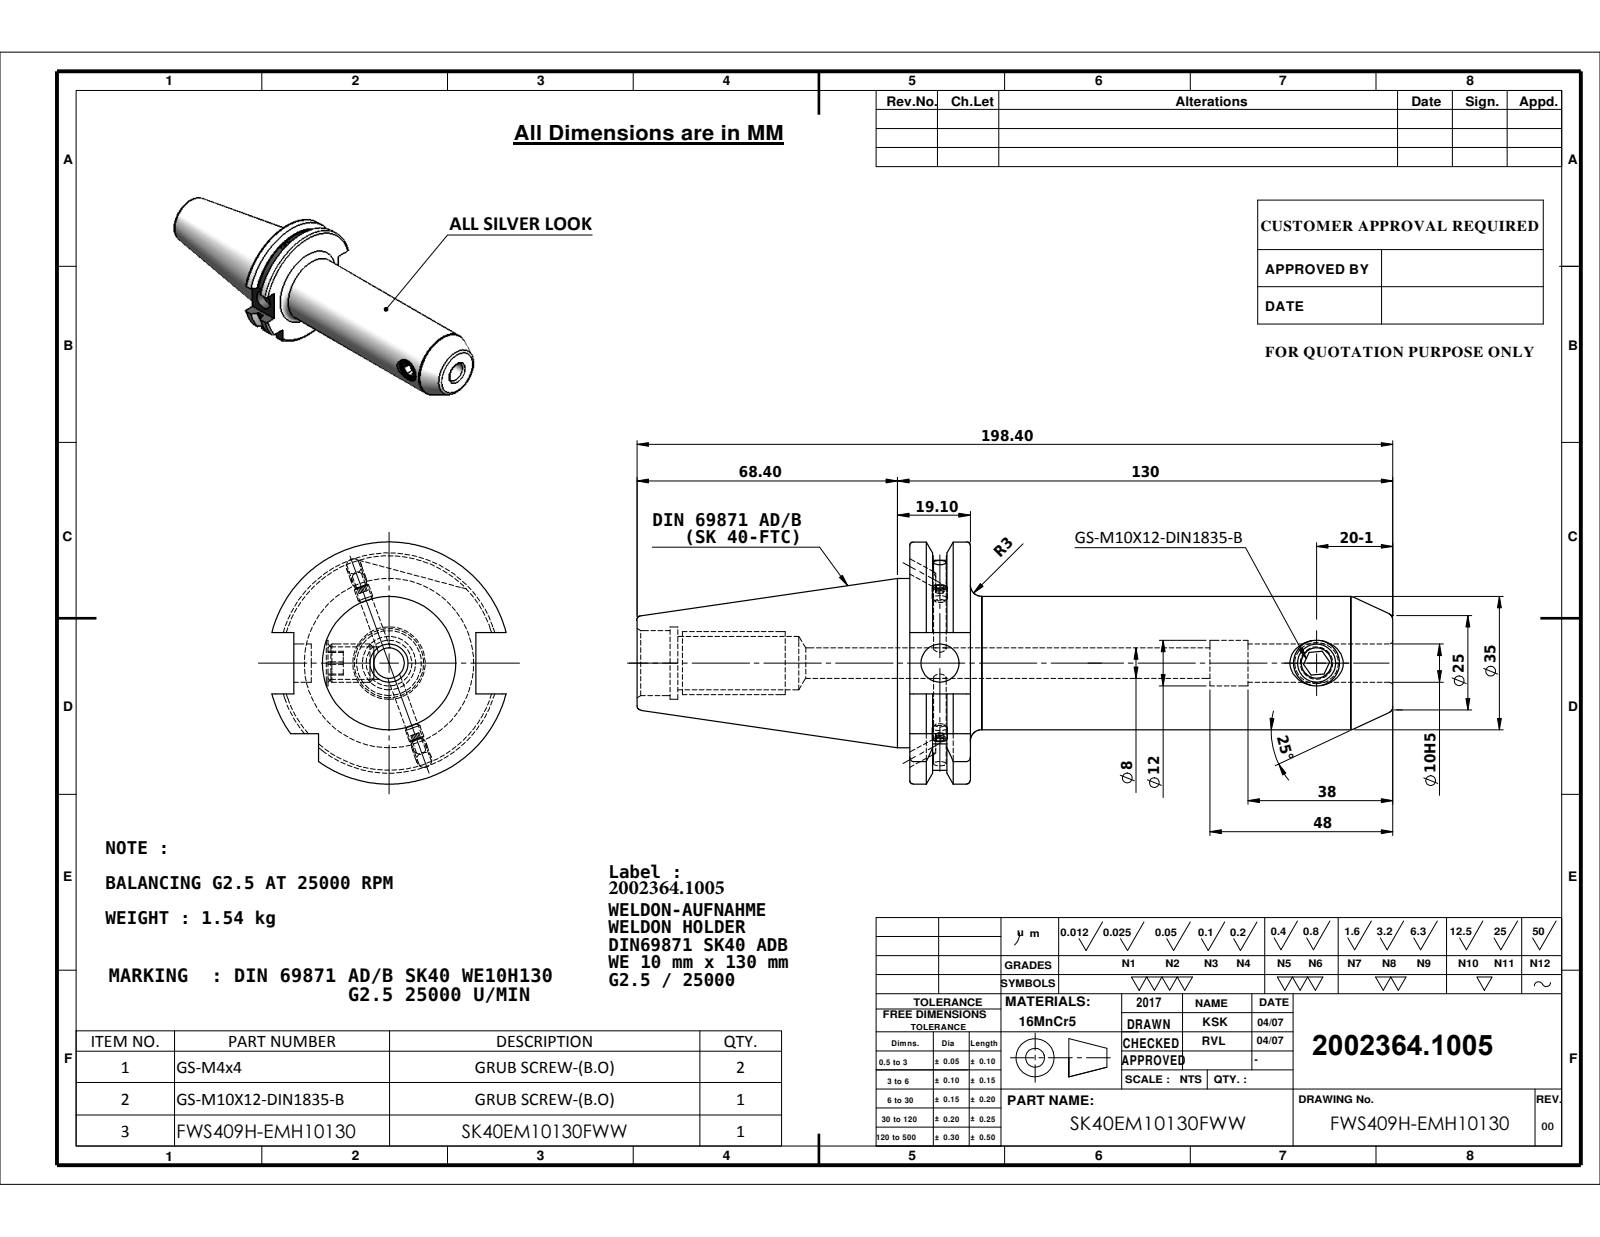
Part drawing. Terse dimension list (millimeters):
name: 91406-WE710130; SK40EM10130FWW; Copy of M4X4_DIN 913 - M4 x 4-N; M10X12
written by: SolidWorks 2009 (CONFIG_CONTROL_DESIGN)
unit: mm
bodies: 4 solids, 159 faces (58 planar, 44 cylindrical, 57 other)
size: 198.4 × 63.55 × 61.48
volume: 199 616 mm³; area: 36 359 mm²
holes: 2× ⌀10, 2× ⌀12, 1× ⌀3.3, 1× ⌀8, 1× ⌀8.5, 1× ⌀14, 1× ⌀17, 1× ⌀19
bosses: 2× ⌀4, 1× ⌀44.45, 1× ⌀35, 1× ⌀10
rounds: 1× R28.12, 1× R31.77
face distances: 15.9, 126.8, 110.9, 16.1, 47.8, 71.6, 87.5, 198.4, 10.7, 60.9
hole spacings: 98.85
